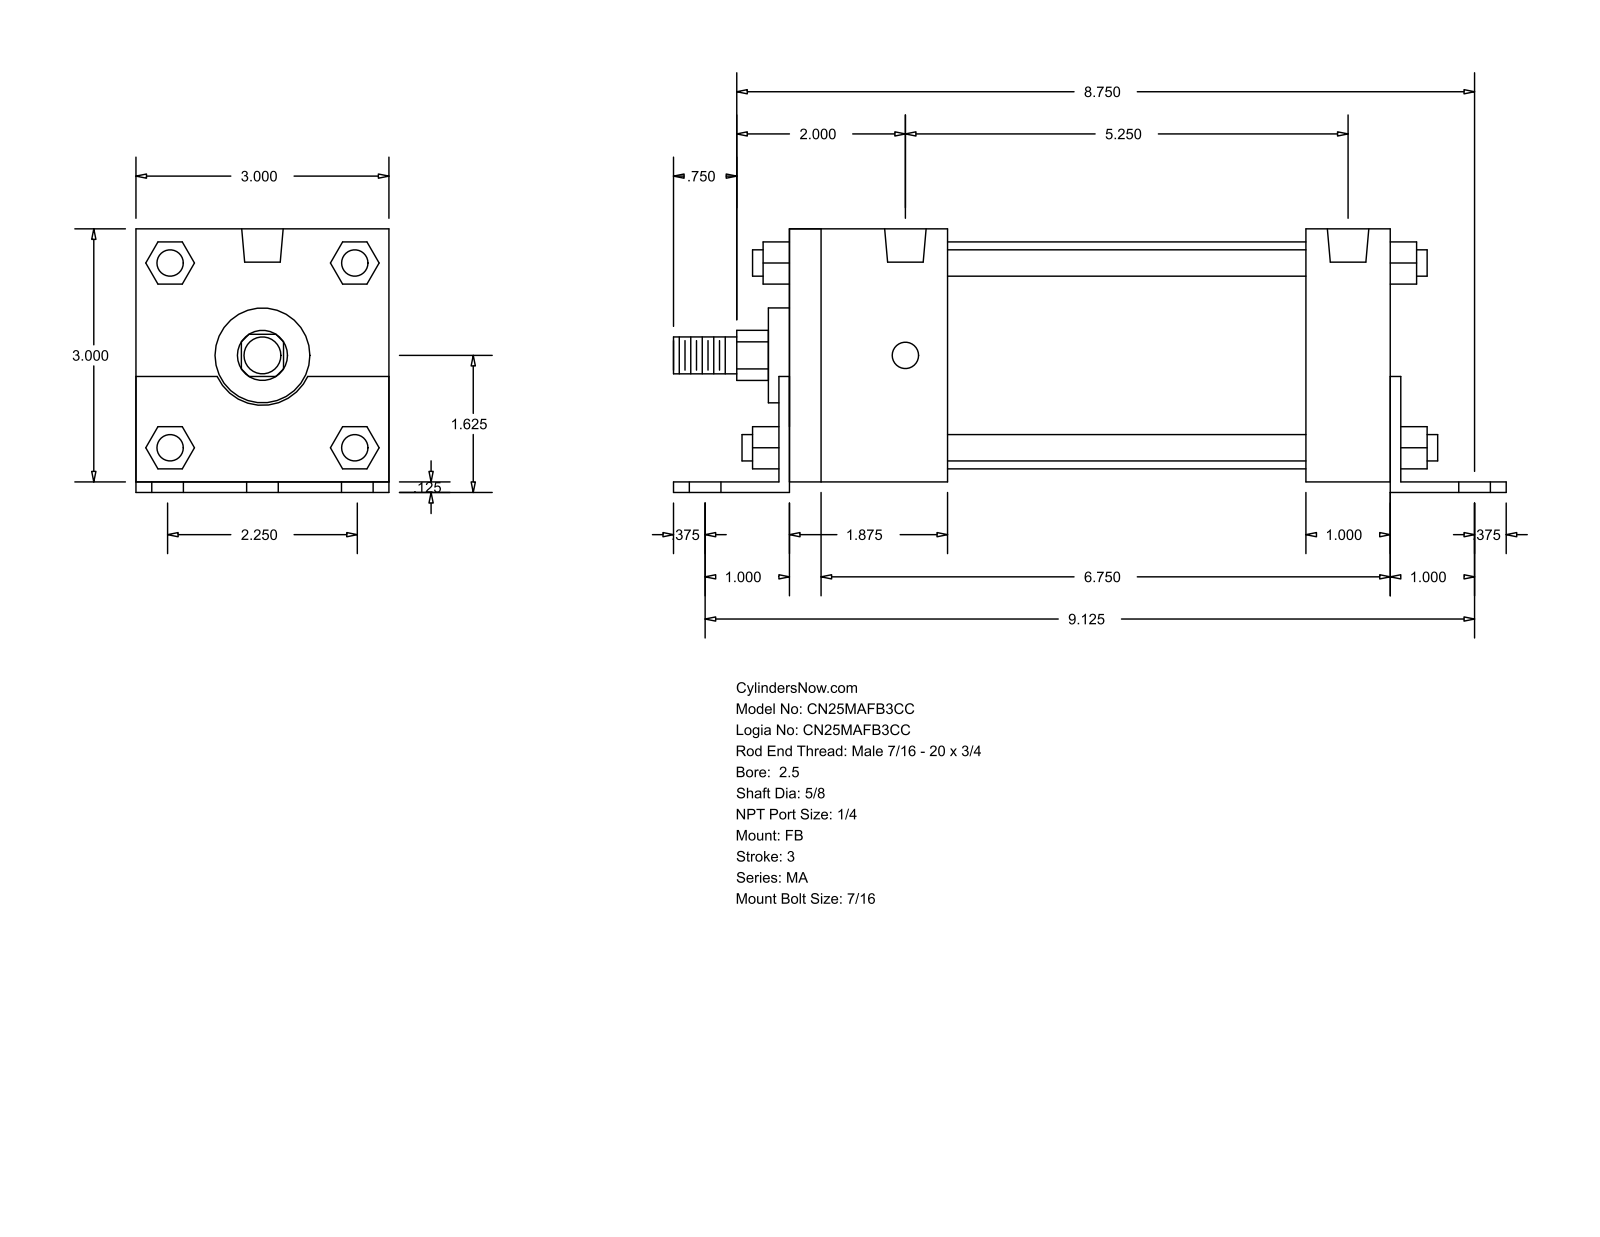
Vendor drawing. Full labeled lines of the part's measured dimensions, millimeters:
Part name (STEP PRODUCT): MA_FB__0250_0.625
STEP written by: GSSL Pune (CONFIG_CONTROL_DESIGN)
Units: millimetres
Bodies: 0 solids, 140 faces (105 planar, 35 cylindrical, 0 other)
Overall size (bounding box): 250.82 × 79.38 × 76.2
Round holes (diameter × count): ⌀11.11 ×6, ⌀7.94 ×4, ⌀12.49 ×2
Round bosses / shafts (diameter × count): ⌀7.94 ×4, ⌀68.33 ×1, ⌀28.57 ×1, ⌀15.88 ×1, ⌀11.11 ×1
Partial cylindrical surfaces — rounded edges, fillets, slot ends (radius × count): R7.54 ×1, R15.05 ×1
Main face-to-face distances: 76.2, 3.17, 79.37, 3.18, 184.15, 180.97, 28.58, 47.62, 25.4, 187.33
Hole centre spacings: 28.57, 233.53, 231.78, 47.62, 57.14, 66.75, 133.35, 173.81
